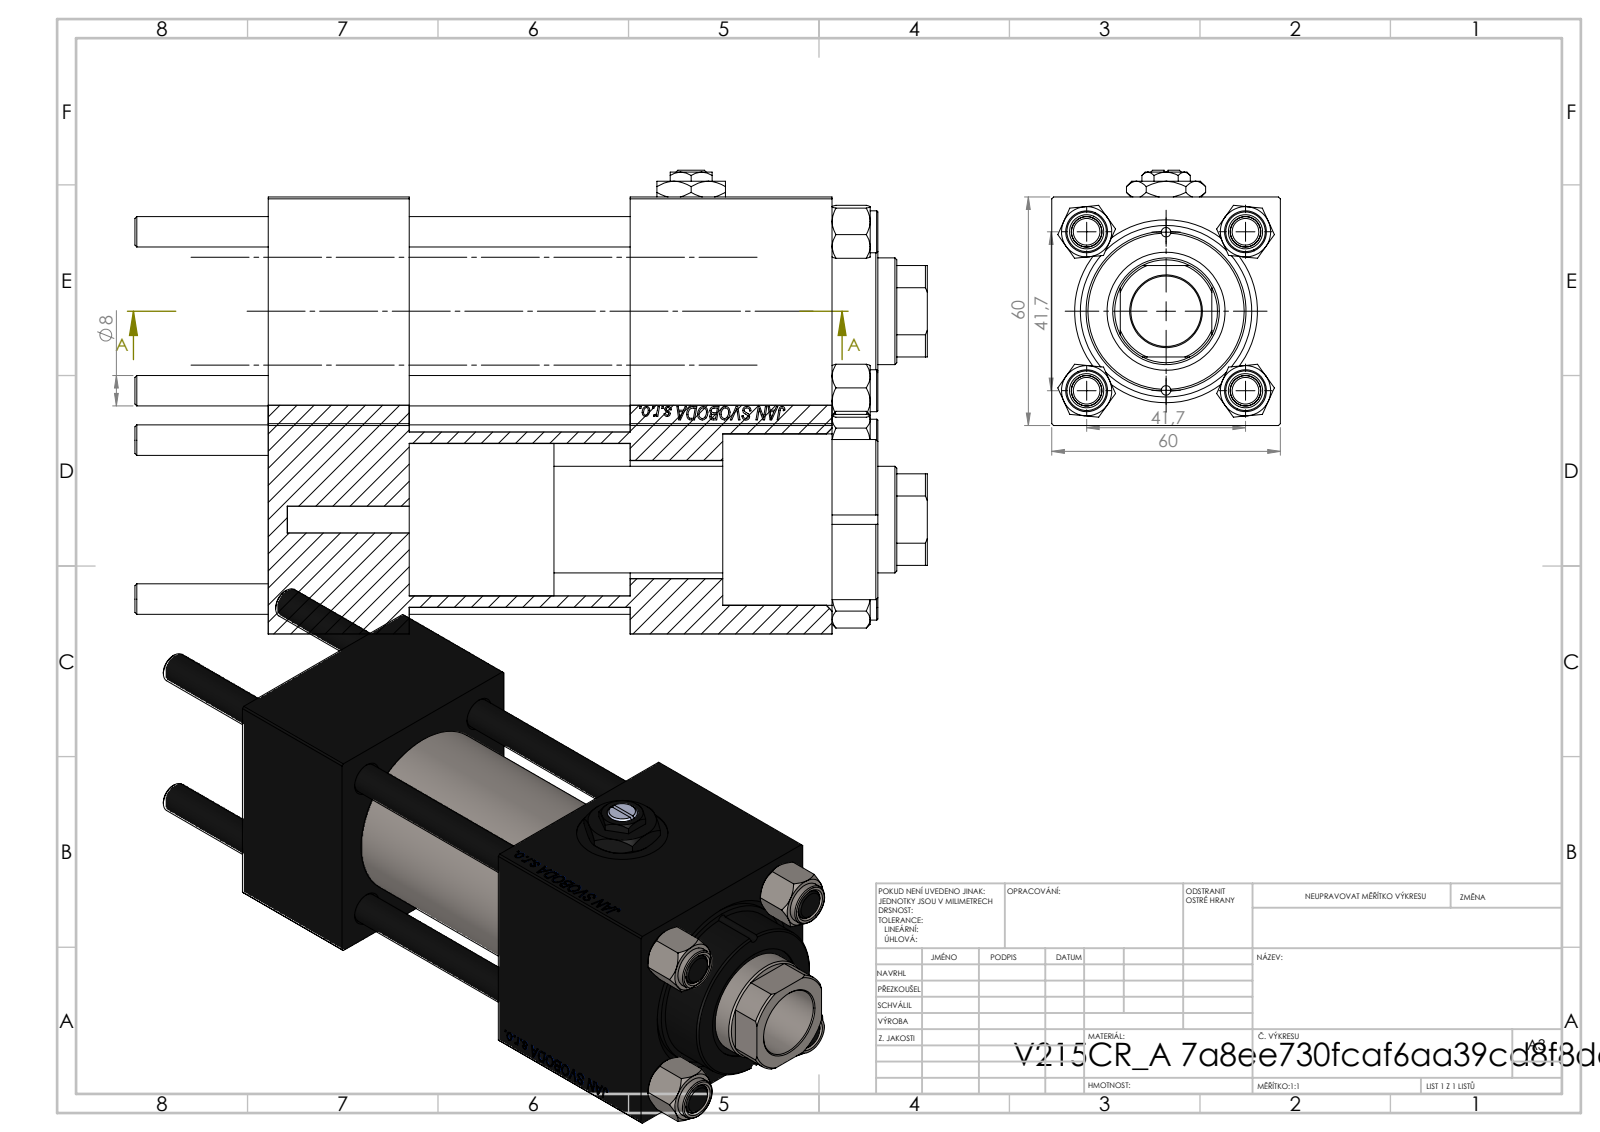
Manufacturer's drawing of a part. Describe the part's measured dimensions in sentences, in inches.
The part is named "Zatka_pro_OIL_PORT; NUT_M5; CR025_012_A_0_G_A_G_M_020_+#_##_TYCINKA; V215CR_BODY_A (+2 more)". Its 3-D file was written by "SolidWorks 2019 (CONFIG_CONTROL_DESIGN)". It is 12 solids with 1189 faces: 547 planar, 86 cylindrical and 556 other. Overall it measures 8.189 by 2.638 by 2.362 inches. Its volume is 26.45 cubic inches and its surface area 188.3 square inches. Round holes: 4 of diameter 0.315, 2 of diameter 0.098, 2 of diameter 0.276, 2 of diameter 0.656, 2 of diameter 0.945, 1 of diameter 0.728, 1 of diameter 1.102, 1 of diameter 1.22, 1 of diameter 1.575, 1 of diameter 1.772. Round bosses or shafts: 4 of diameter 0.433, 1 of diameter 1.811, 1 of diameter 1.654. Partial cylindrical surfaces (rounded edges, fillets, slot ends): 1 of radius 0.531. The main face-to-face distances are 2.362, 1.457, 2.283, 3.74, 2.087, 5.827, 4.37, 4.697, 3.24, 0.957. The hole center spacings are 0.821, 1.161, 1.642, 1.832, 0.817, 2.322, 1.634, 3.642.
